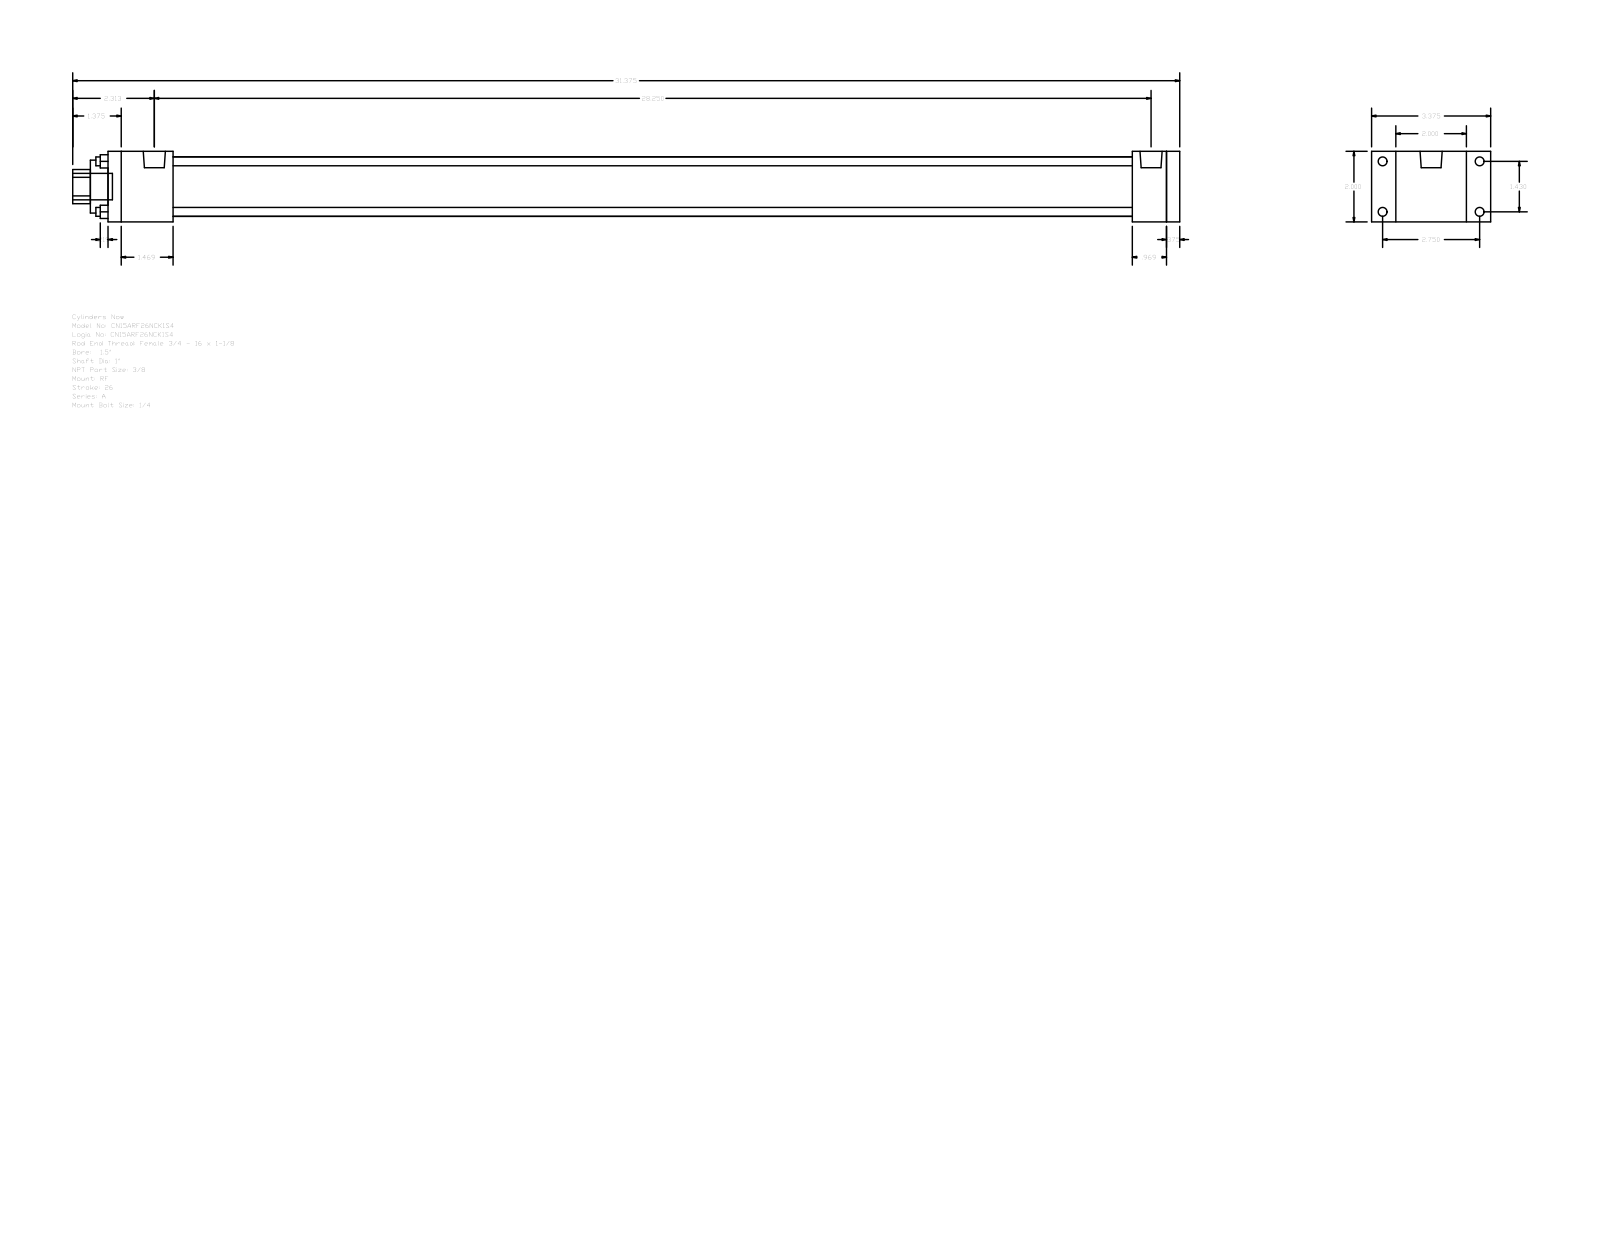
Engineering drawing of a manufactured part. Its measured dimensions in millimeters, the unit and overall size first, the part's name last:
Units: millimetres
Overall size (bounding box): 796.92 × 85.72 × 50.8
Round holes (diameter × count): ⌀6.35 ×4, ⌀25.4 ×1, ⌀38.1 ×1, ⌀42.93 ×1
Round bosses / shafts (diameter × count): ⌀6.35 ×4, ⌀5.56 ×4, ⌀15.93 ×2, ⌀19.05 ×1
Partial cylindrical surfaces — rounded edges, fillets, slot ends (radius × count): R12.29 ×1
Main face-to-face distances: 50.8, 9.52, 762, 771.52, 737.39, 24.61, 34.13, 46.83, 690.56, 715.17
Hole centre spacings: 25.68, 36.32, 51.36
Bodies: 0 solids, 92 faces (64 planar, 28 cylindrical, 0 other)
Part name (STEP PRODUCT): A_RF__0150_1
STEP written by: GSSL Pune (CONFIG_CONTROL_DESIGN)
